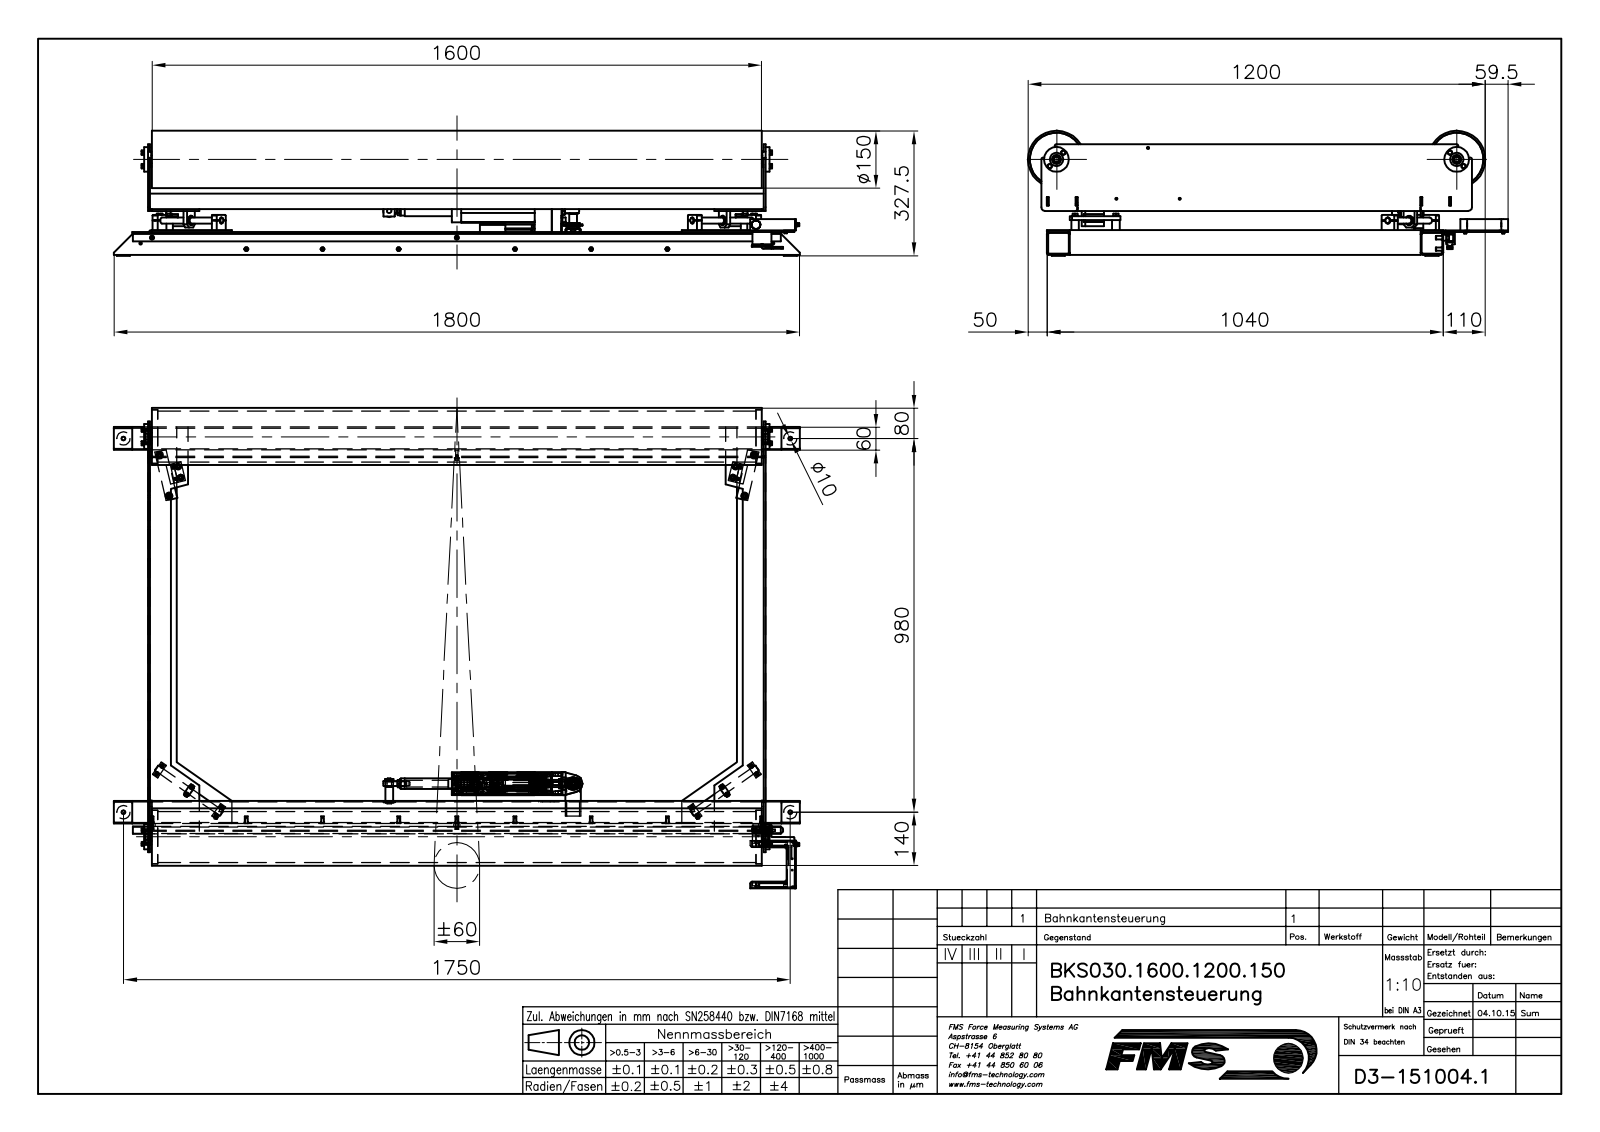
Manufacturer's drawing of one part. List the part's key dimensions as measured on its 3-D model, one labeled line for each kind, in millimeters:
Part name (STEP PRODUCT): K1510041; K1510042; K1510044; K1510045 (+8 more)
STEP written by: Mechanical Desktop 2009 (CONFIG_CONTROL_DESIGN)
Units: millimetres
Bodies: 164 solids, 2798 faces (1315 planar, 1039 cylindrical, 444 other)
Overall size (bounding box): 1800 × 1259.5 × 327.5
Volume: 21 910 000 mm³ · Surface area: 8 375 000 mm²
Round holes (diameter × count): ⌀5.15 ×35, ⌀7 ×18, ⌀4.3 ×12, ⌀11 ×11, ⌀8.4 ×10, ⌀6.4 ×9, ⌀10 ×8, ⌀3.42 ×6, ⌀16 ×6, ⌀2.6 ×4, ⌀3.2 ×4, ⌀5.5 ×4
Round bosses / shafts (diameter × count): ⌀6 ×21, ⌀9 ×17, ⌀10 ×15, ⌀8 ×13, ⌀16 ×11, ⌀12 ×11, ⌀4 ×10, ⌀20 ×8
Partial cylindrical surfaces — rounded edges, fillets, slot ends (radius × count): R1 ×22, R2 ×19, R5 ×19, R4 ×16, R3 ×8, R6 ×8, R10 ×6, R0.4 ×4
Main face-to-face distances: 3, 5, 60, 57, 980, 37, 63, 100, 1616, 120
Hole centre spacings: 30, 200, 202.24, 95, 24, 705, 705.64, 97.98
